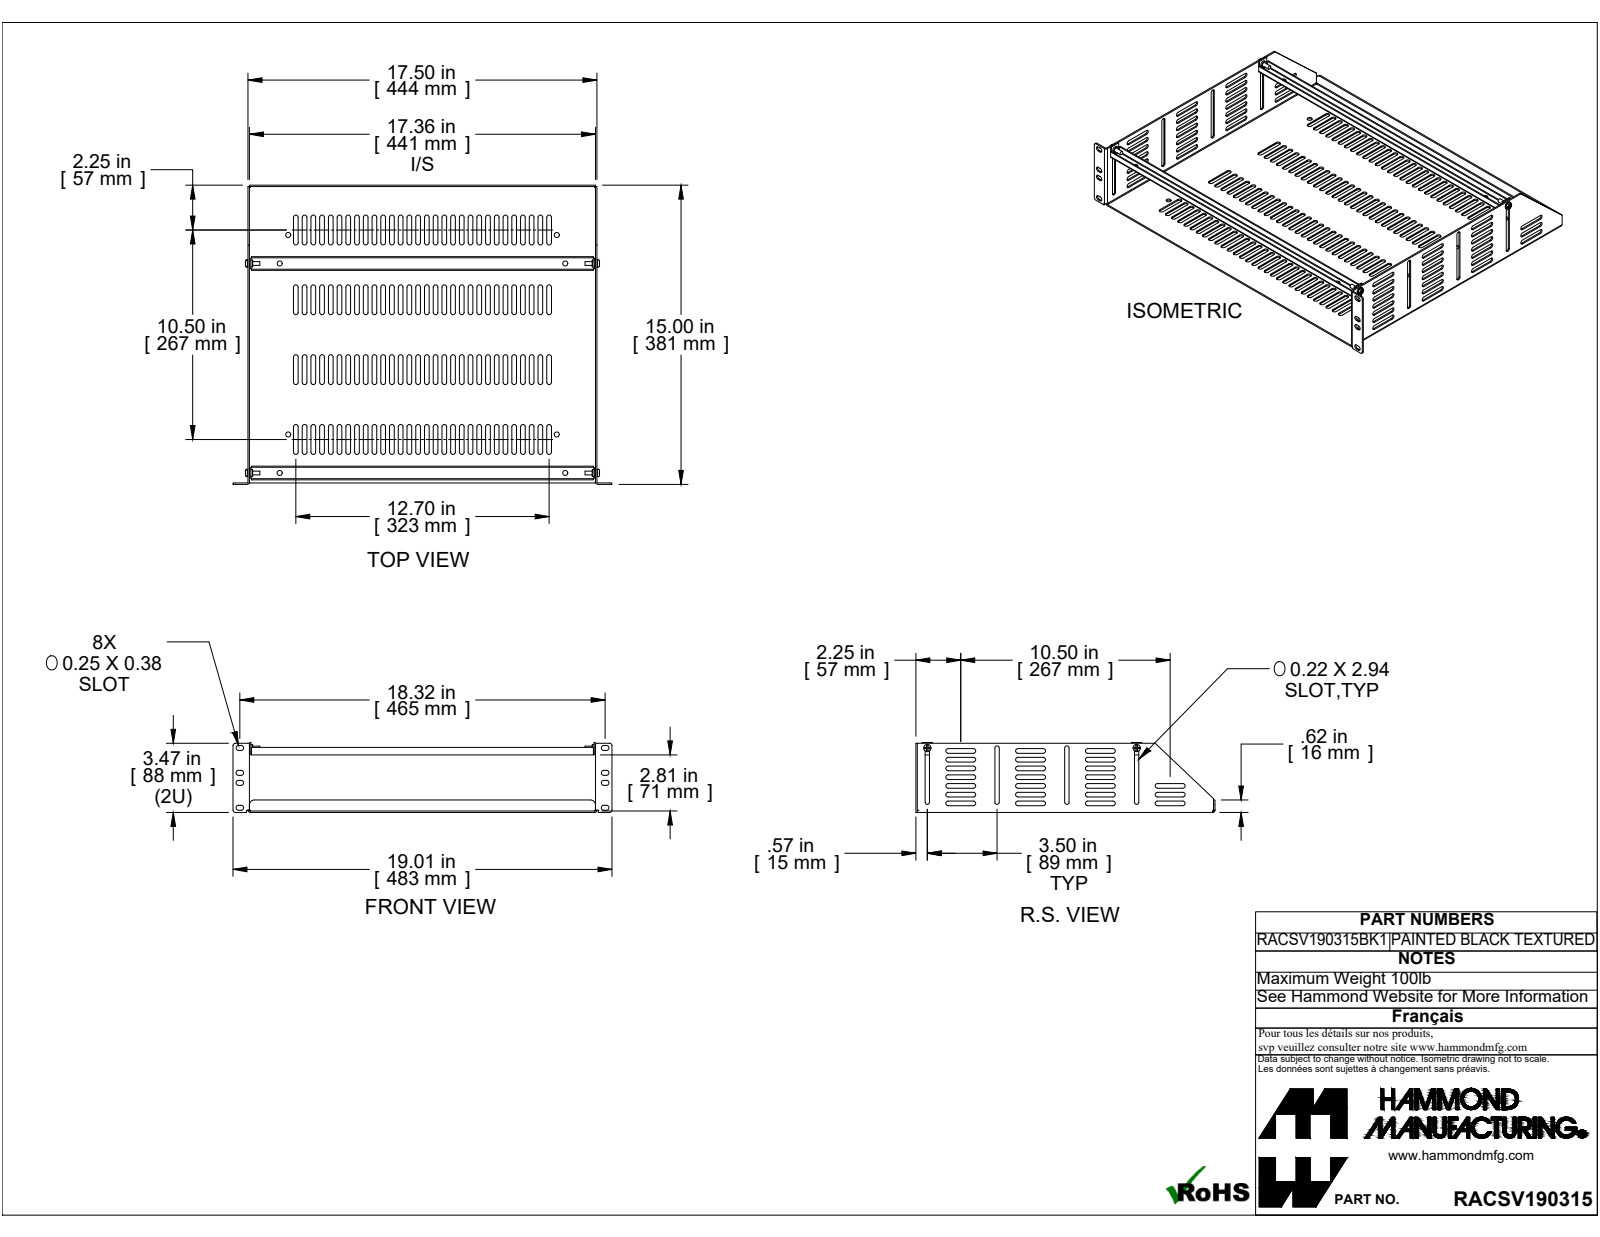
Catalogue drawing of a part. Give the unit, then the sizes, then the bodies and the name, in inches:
Units: inches
Overall size (bounding box): 19.006 × 15 × 3.508
Round holes (diameter × count): ⌀0.25 ×6, ⌀0.159 ×2
Round bosses / shafts (diameter × count): ⌀0.368 ×2, ⌀0.34 ×2, ⌀0.244 ×2, ⌀0.189 ×2
Partial cylindrical surfaces — rounded edges, fillets, slot ends (radius × count): R0.118 ×280, R0.125 ×20, R0.109 ×8, R0.117 ×8, R0.029 ×6, R0.086 ×6, R0.036 ×5, R0.108 ×5
Main face-to-face distances: 0.072, 17.428, 0.057, 17.5, 17.356, 10.5, 0.631, 2.885, 2.942, 2.813
Hole centre spacings: 10, 13.468, 16.774, 10.5
Volume: 24.61 in³ · Surface area: 757.3 in²
Bodies: 11 solids, 986 faces (534 planar, 436 cylindrical, 16 other)
Part name (STEP PRODUCT): RACSV190315
STEP written by: SolidWorks 2019 (CONFIG_CONTROL_DESIGN)
